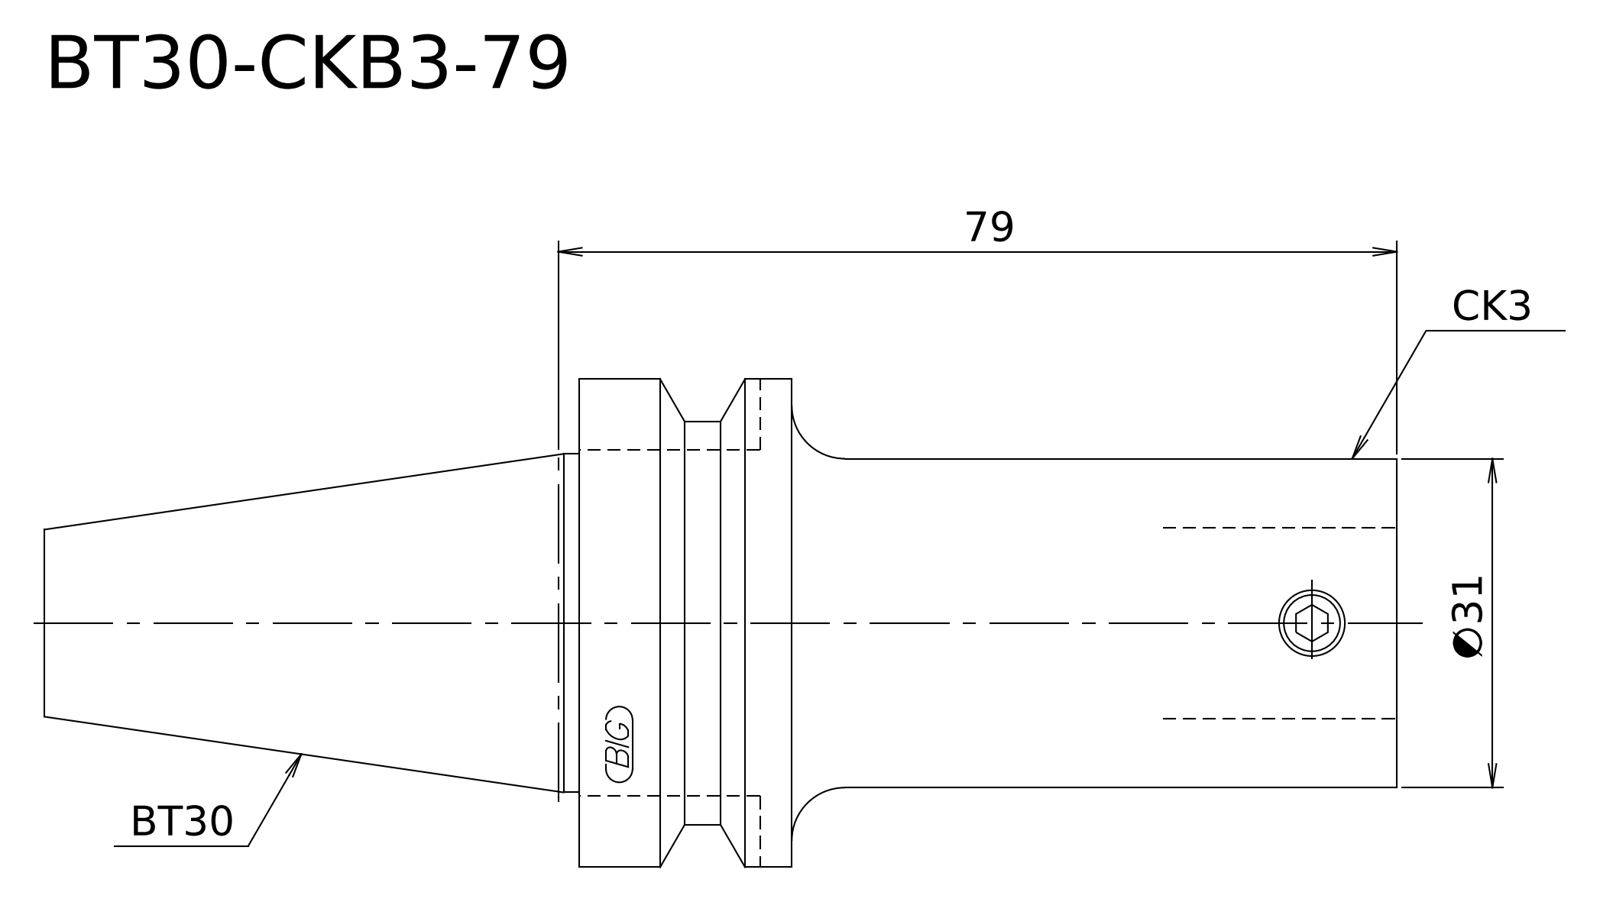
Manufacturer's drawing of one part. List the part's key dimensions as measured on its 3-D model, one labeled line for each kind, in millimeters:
STEP written by: Kubotek KeyCreator V8.5.1 (14335) (CONFIG_CONTROL_DESIGN)
Units: millimetres
Bodies: 1 solid, 13 faces (4 planar, 5 cylindrical, 4 other)
Overall size (bounding box): 127.4 × 46 × 46
Volume: 99 969 mm³ · Surface area: 15 419 mm²
Round bosses / shafts (diameter × count): ⌀46 ×1, ⌀38 ×1, ⌀31.9 ×1, ⌀31 ×1
Main face-to-face distances: 77, 57, 20, 127.4, 70.4, 50.4
